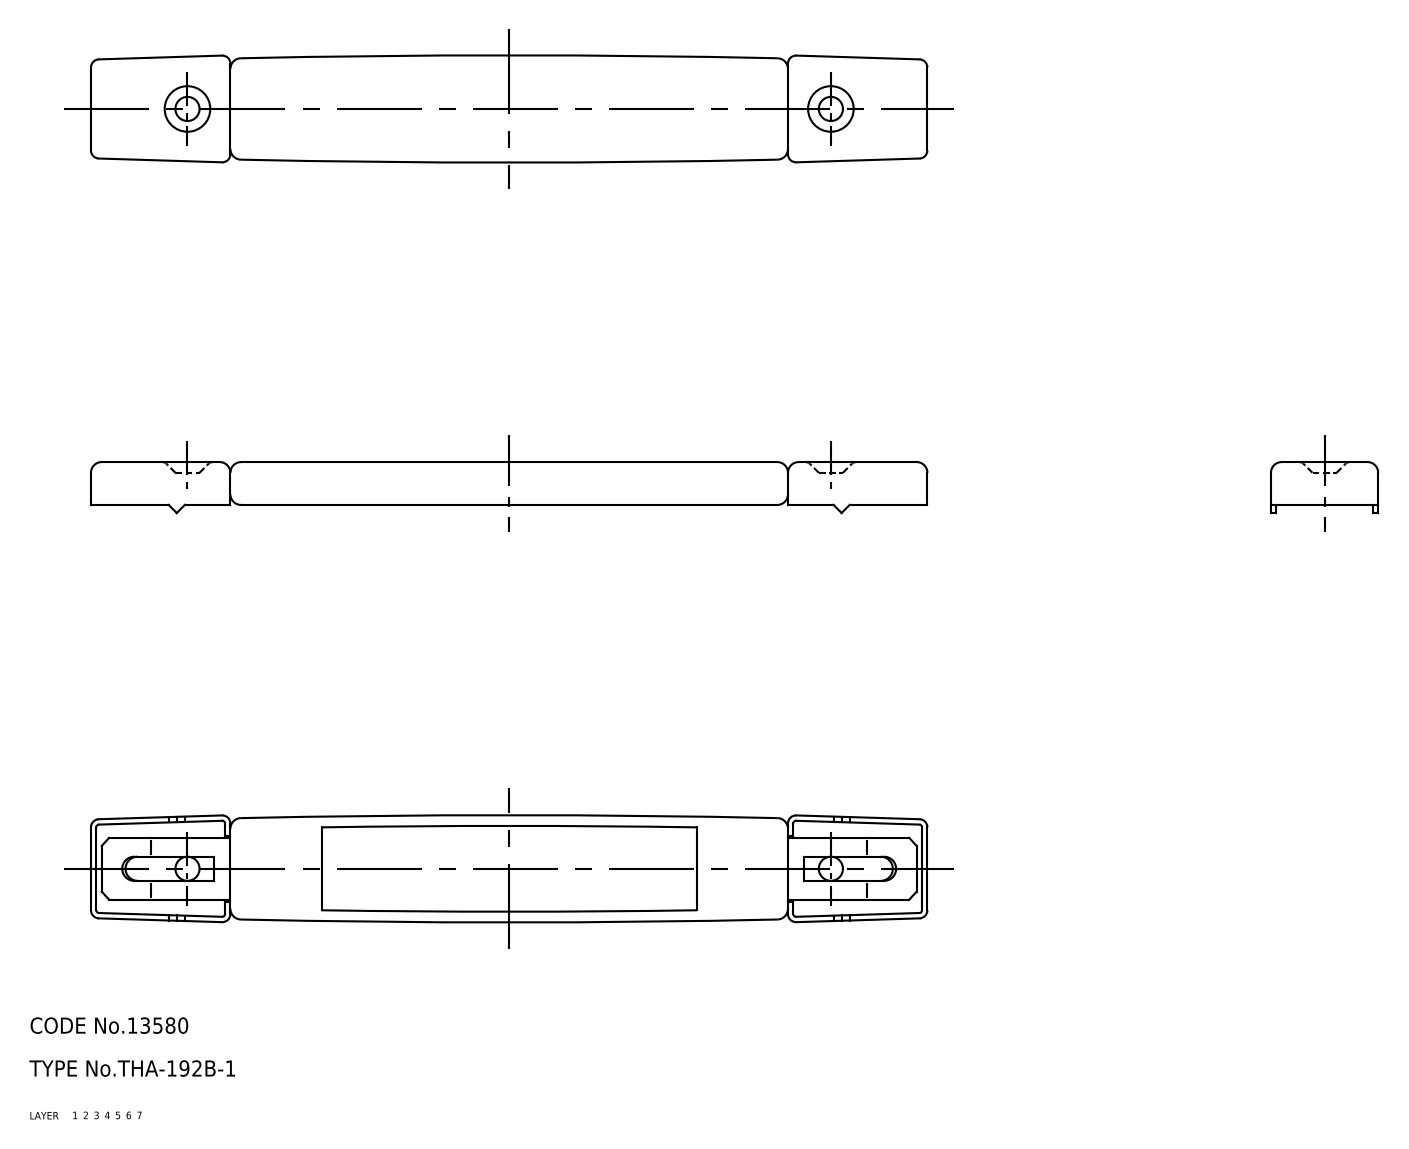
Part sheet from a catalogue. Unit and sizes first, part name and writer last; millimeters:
Units: millimetres
Overall size (bounding box): 156 × 20 × 9.5
Volume: 17 085 mm³ · Surface area: 14 757 mm²
Bodies: 5 solids, 170 faces (0 planar, 0 cylindrical, 170 other)
Part name (STEP PRODUCT): 67116313; 67116326; 67116339; 67116352 (+1 more)
STEP written by: CADfix (AUTOMOTIVE_DESIGN)
